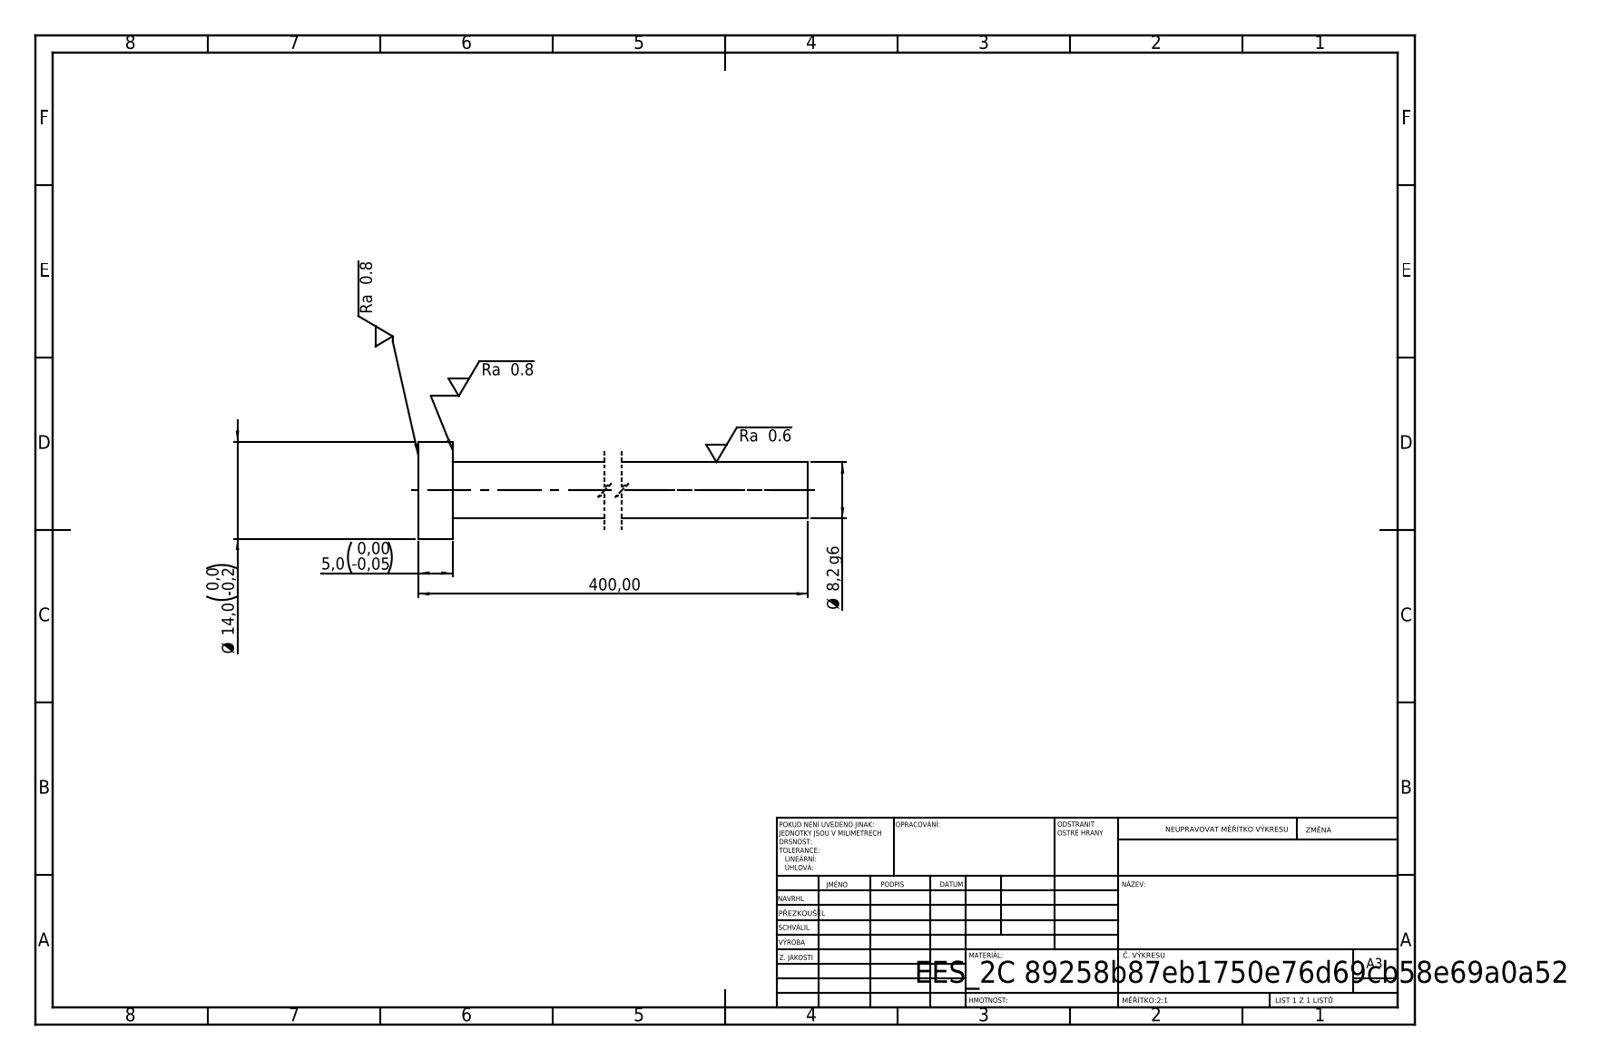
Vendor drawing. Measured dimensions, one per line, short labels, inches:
written by: SolidWorks 2019 (CONFIG_CONTROL_DESIGN)
unit: in
bodies: 1 solid, 7 faces (3 planar, 4 cylindrical, 0 other)
size: 15.748 × 0.551 × 0.551
volume: 1.32 in³; area: 16.59 in²
bosses: 1× ⌀0.551, 1× ⌀0.323
face distances: 0.197, 15.748, 15.551
